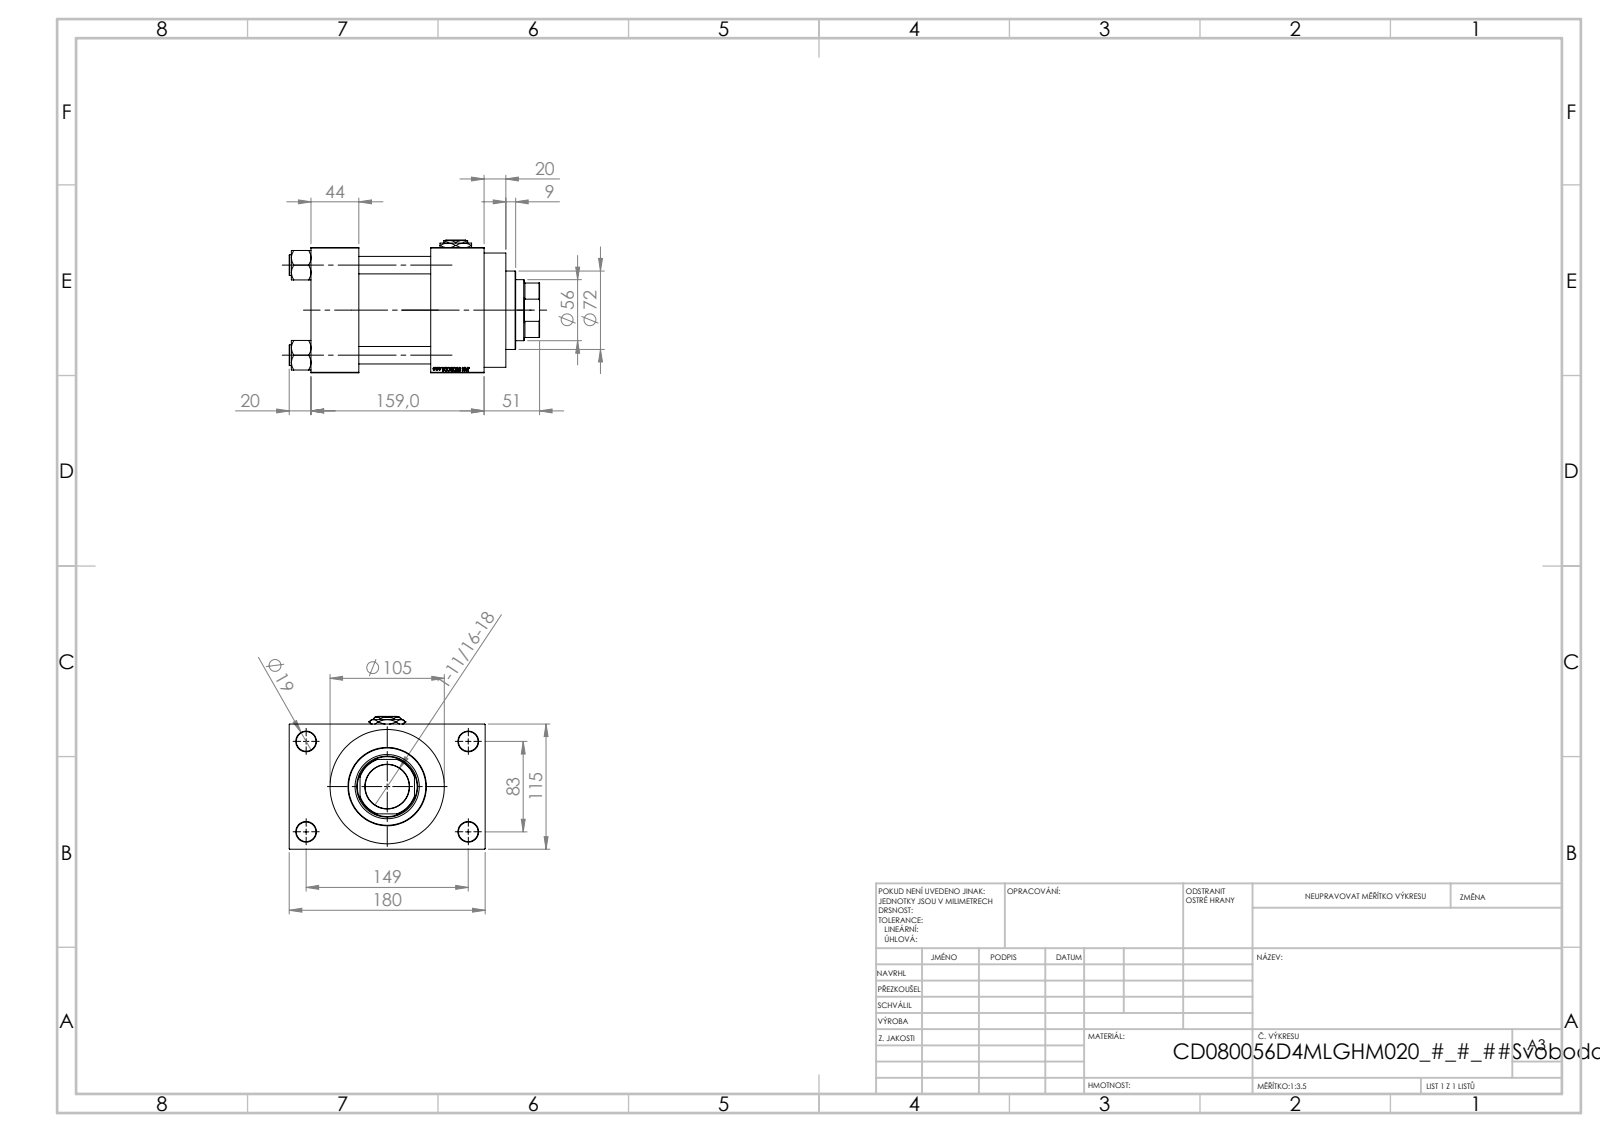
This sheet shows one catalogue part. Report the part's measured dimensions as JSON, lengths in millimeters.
{"part_name": "V215CD_VCP_D; V215CD_VC_A; V215CD_NUT_M5_D; Zatka_pro_OIL_PORT (+2 more)", "step_written_by": "SolidWorks 2019 (CONFIG_CONTROL_DESIGN)", "units": "millimeters", "bodies": {"solids": 12, "faces": 1191, "planar": 566, "cylindrical": 87, "other": 538}, "overall_size": [230, 180, 122], "volume_mm3": 2123000, "surface_area_mm2": 310054, "round_holes": [[16, 4], [18, 4], [7, 2], [26.44, 2], [35, 2], [40.5, 1], [56, 1], [59, 1], [61, 1], [72, 1], [80, 1]], "round_bosses_or_shafts": [[19, 4], [105, 1], [86, 1]], "partial_cylinders_radius": [[27, 1]], "face_to_face_distances": [115, 66, 110, 44, 32.5, 159, 49, 147.5, 20, 69], "hole_center_spacings": [33.15, 58.48, 82.7, 85.28, 89.24, 115.85, 142.43, 83]}
